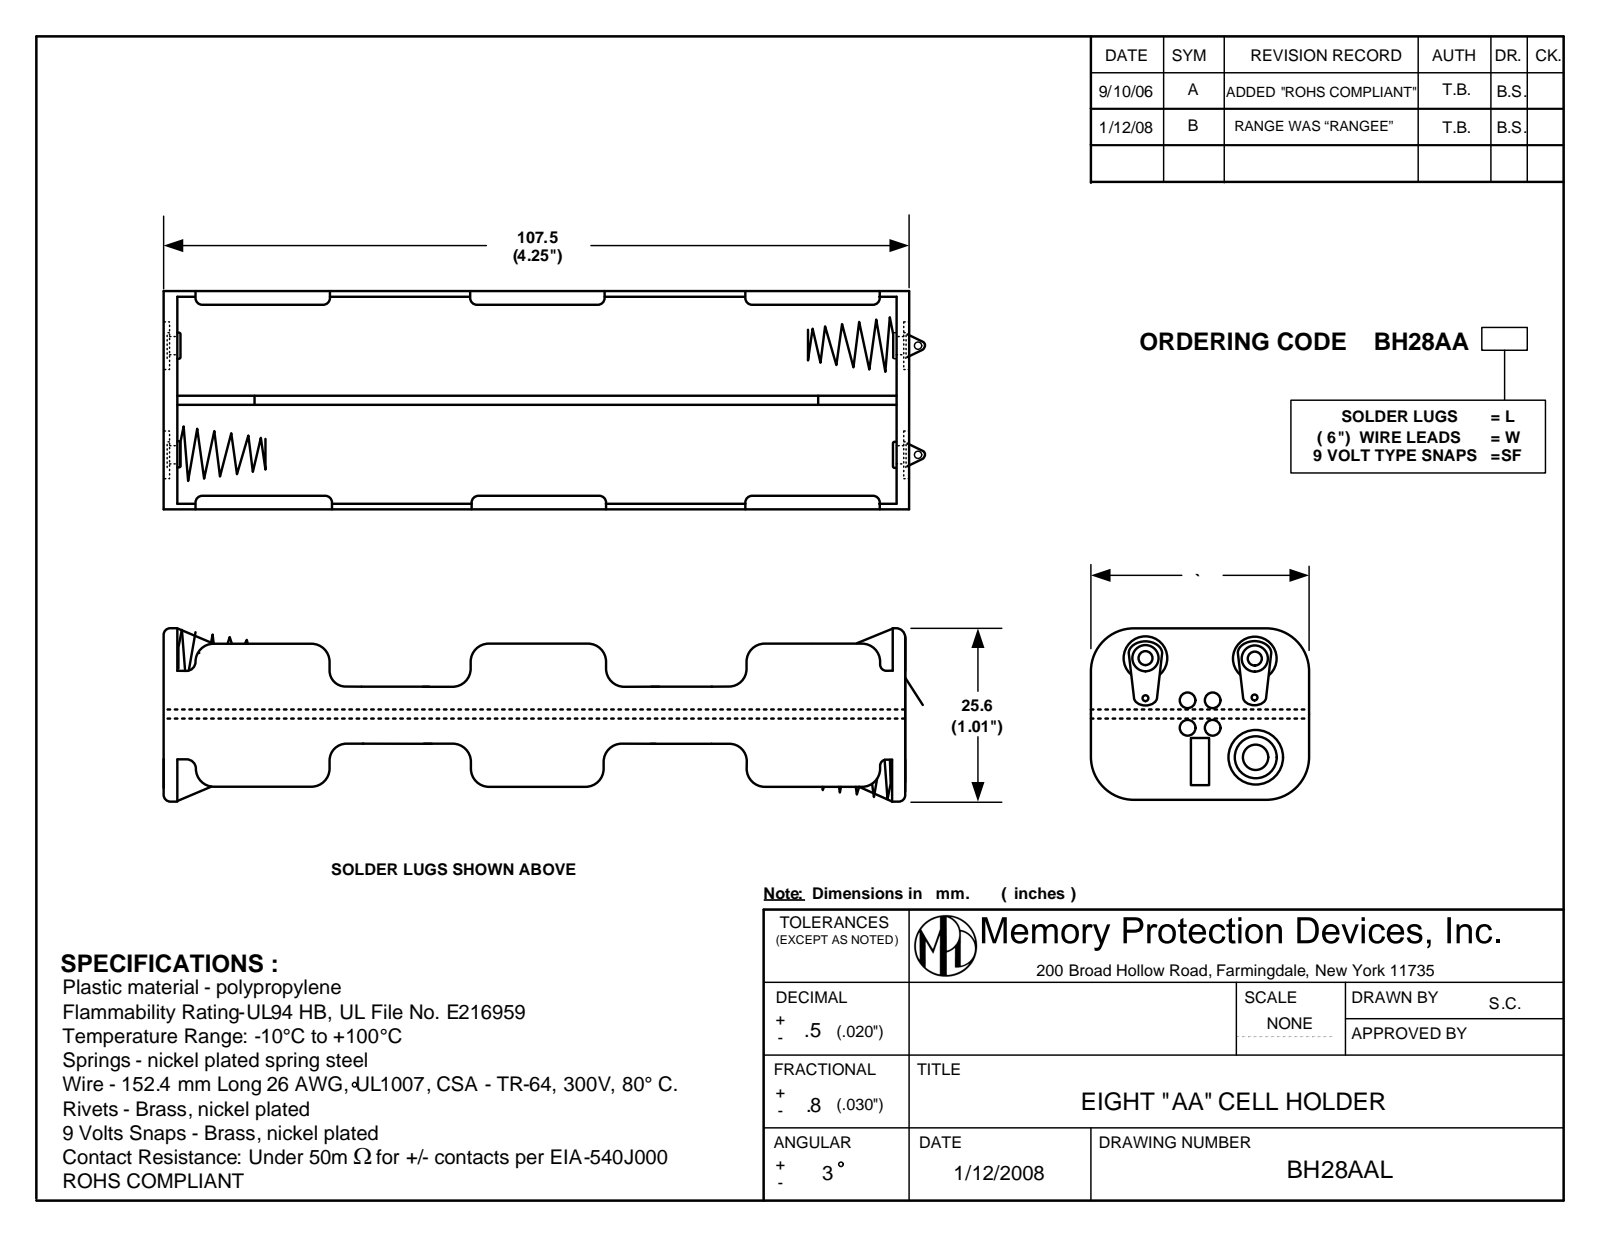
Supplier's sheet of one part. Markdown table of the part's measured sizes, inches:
| quantity | value |
| --- | --- |
| part name | BH28AAL |
| STEP written by | SolidWorks 2012 (CONFIG_CONTROL_DESIGN) |
| units | inches |
| bodies | 1 solid, 10 faces (6 planar, 4 cylindrical, 0 other) |
| overall size | 4.25 × 1.22 × 1.01 |
| volume | 5.091 in³ |
| surface area | 19.89 in² |
| partial cylindrical surfaces (radius × count) | 0.2 × 4 |
| main face-to-face distances | 1.01, 1.22, 4.25 |
